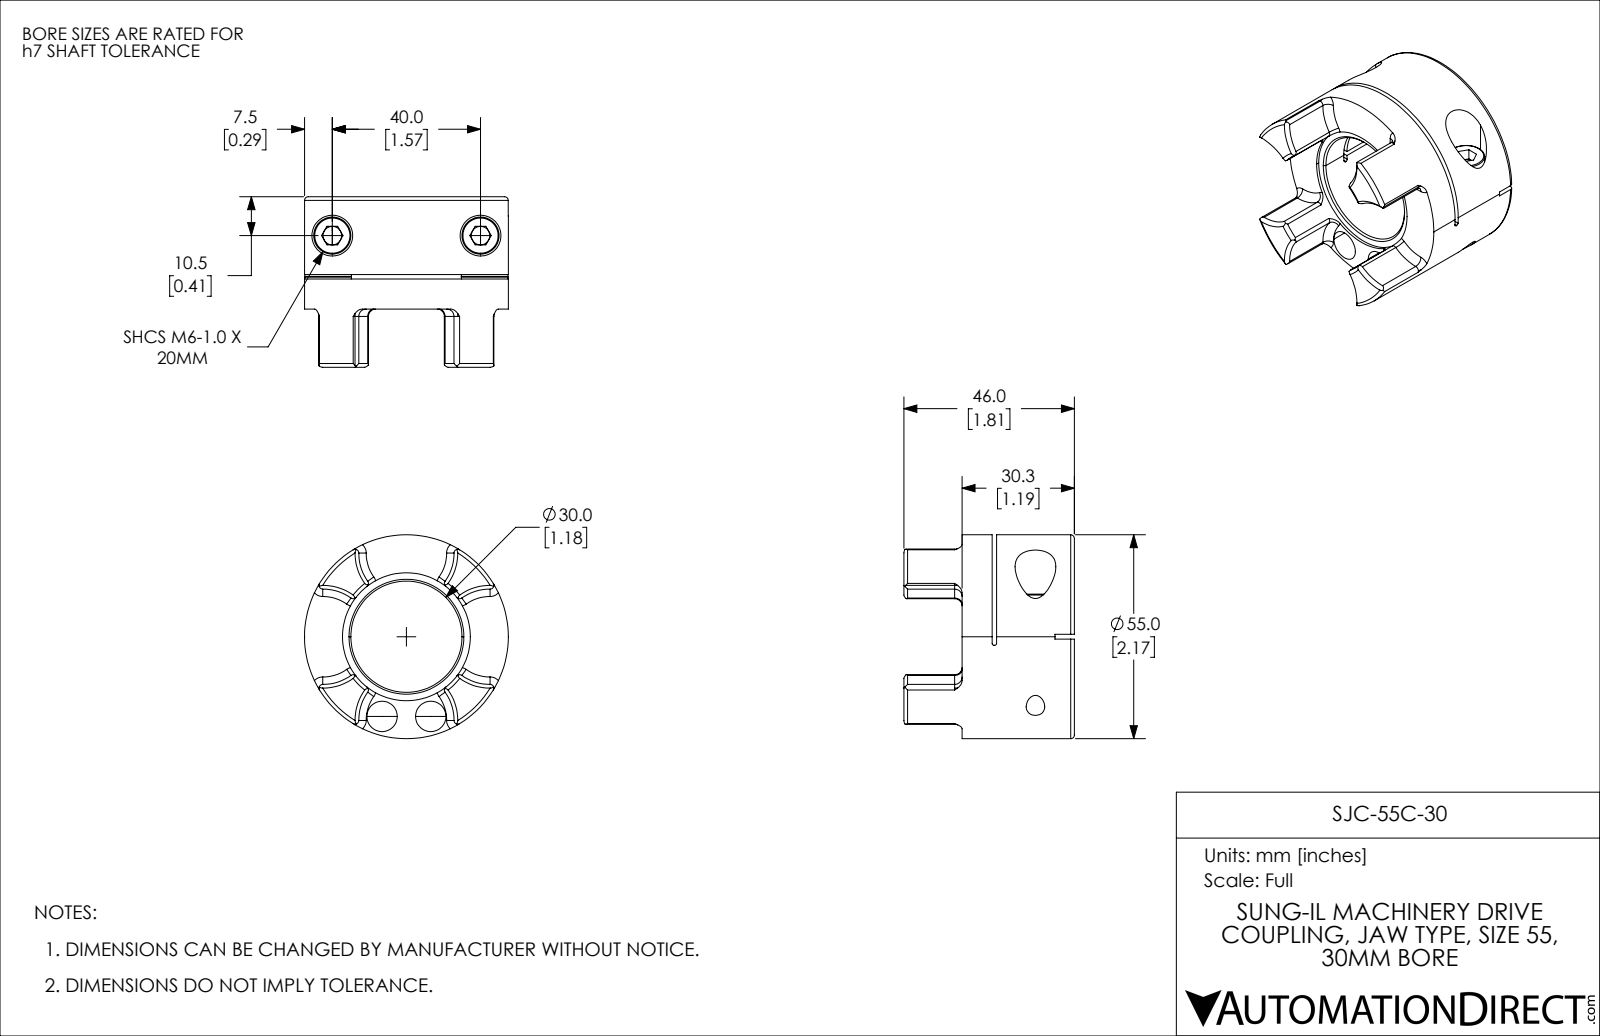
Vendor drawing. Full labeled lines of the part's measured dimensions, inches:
Part name (STEP PRODUCT): SJC-55C-30
STEP written by: SolidWorks 2021 (CONFIG_CONTROL_DESIGN)
Units: inches
Bodies: 3 solids, 206 faces (52 planar, 72 cylindrical, 82 other)
Overall size (bounding box): 2.165 × 2.165 × 1.811
Volume: 3.183 in³ · Surface area: 30.21 in²
Round holes (diameter × count): ⌀0.197 ×2, ⌀0.252 ×2, ⌀0.323 ×2, ⌀0.433 ×2, ⌀1.181 ×1, ⌀1.358 ×1
Round bosses / shafts (diameter × count): ⌀0.394 ×2, ⌀0.236 ×2, ⌀2.165 ×1
Partial cylindrical surfaces — rounded edges, fillets, slot ends (radius × count): R0.039 ×16, R0.506 ×4, R0.02 ×2, R1.969 ×1
Main face-to-face distances: 0.874, 0.047, 0.827, 0.319, 0.366, 1.193, 0.051, 0.618, 0.937, 0.984
Hole centre spacings: 0.885, 0.517, 1.575
